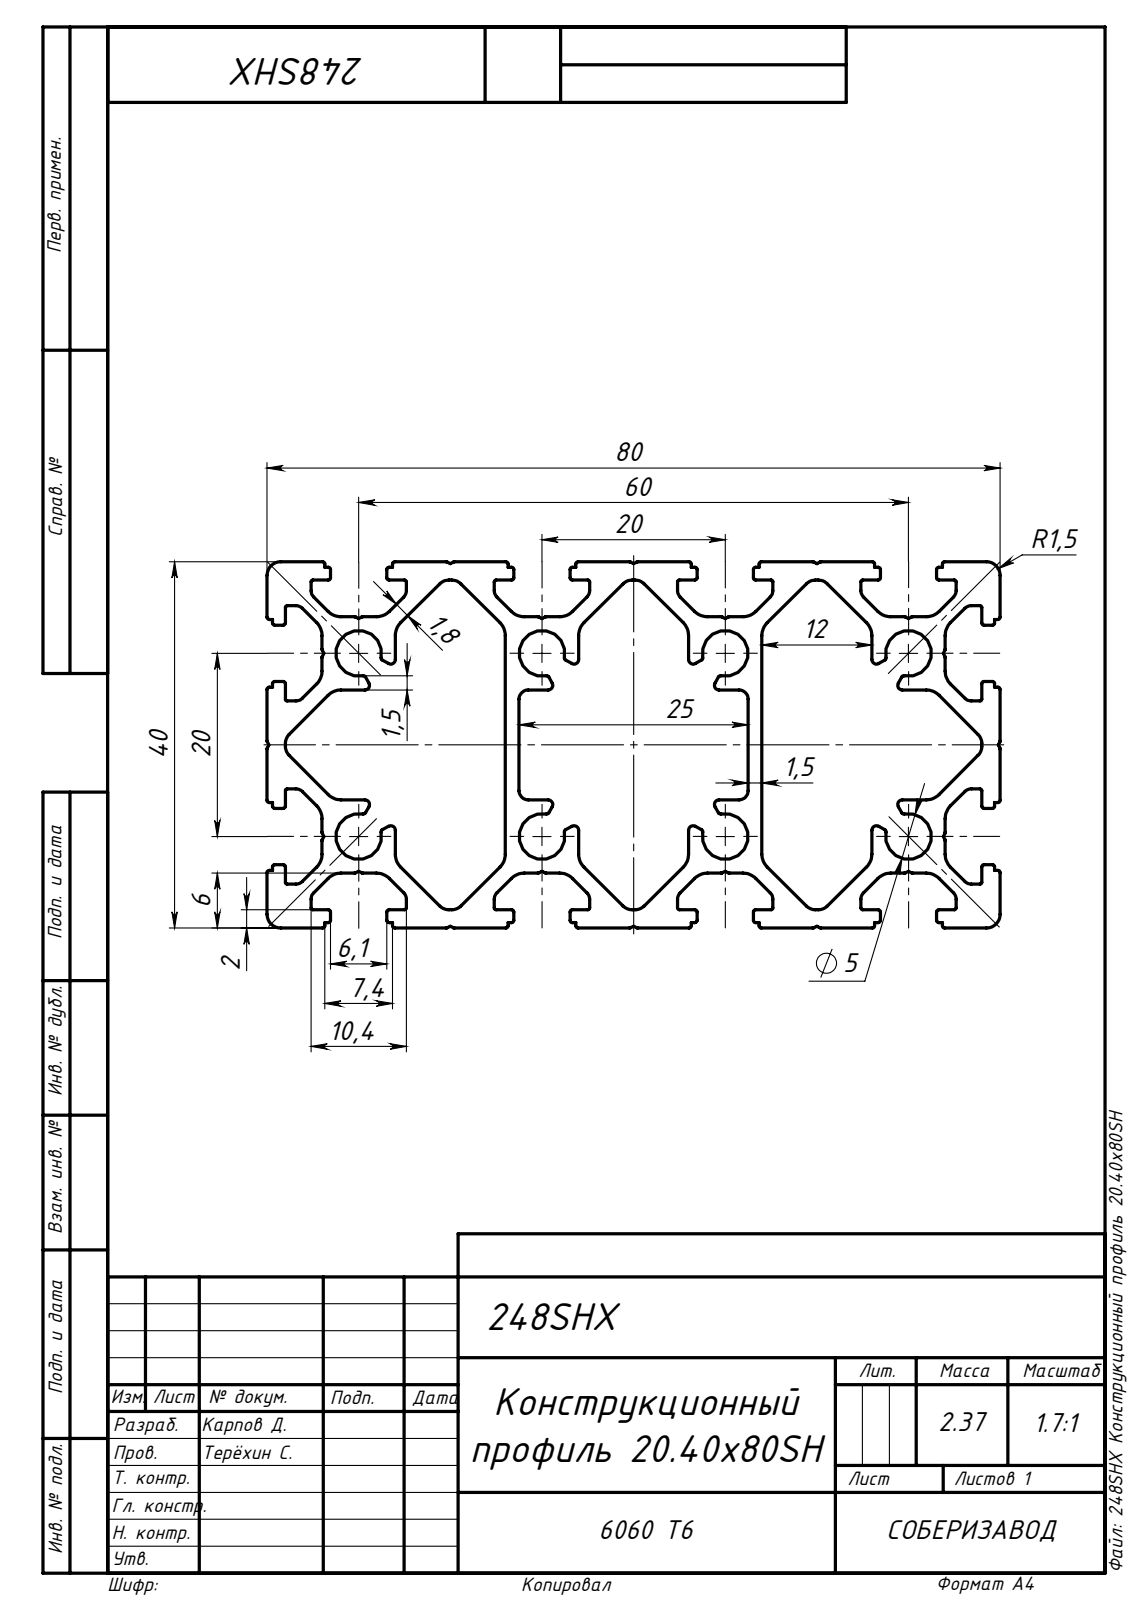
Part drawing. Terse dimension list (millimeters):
written by: SolidWorks 2019 (AUTOMOTIVE_DESIGN)
unit: mm
bodies: 1 solid, 578 faces (294 planar, 284 cylindrical, 0 other)
size: 1000 × 80 × 40
volume: 876 196 mm³; area: 831 469 mm²
holes: 8× ⌀5
rounds: 128× R0.25, 40× R2, 28× R1, 24× R0.2, 16× R0.5, 16× R1.4, 4× R1.5
face distances: 40, 20, 26, 12, 14.1, 28, 32, 2, 54, 26.54
hole spacings: 20, 28.28, 40, 44.72, 60, 63.25
